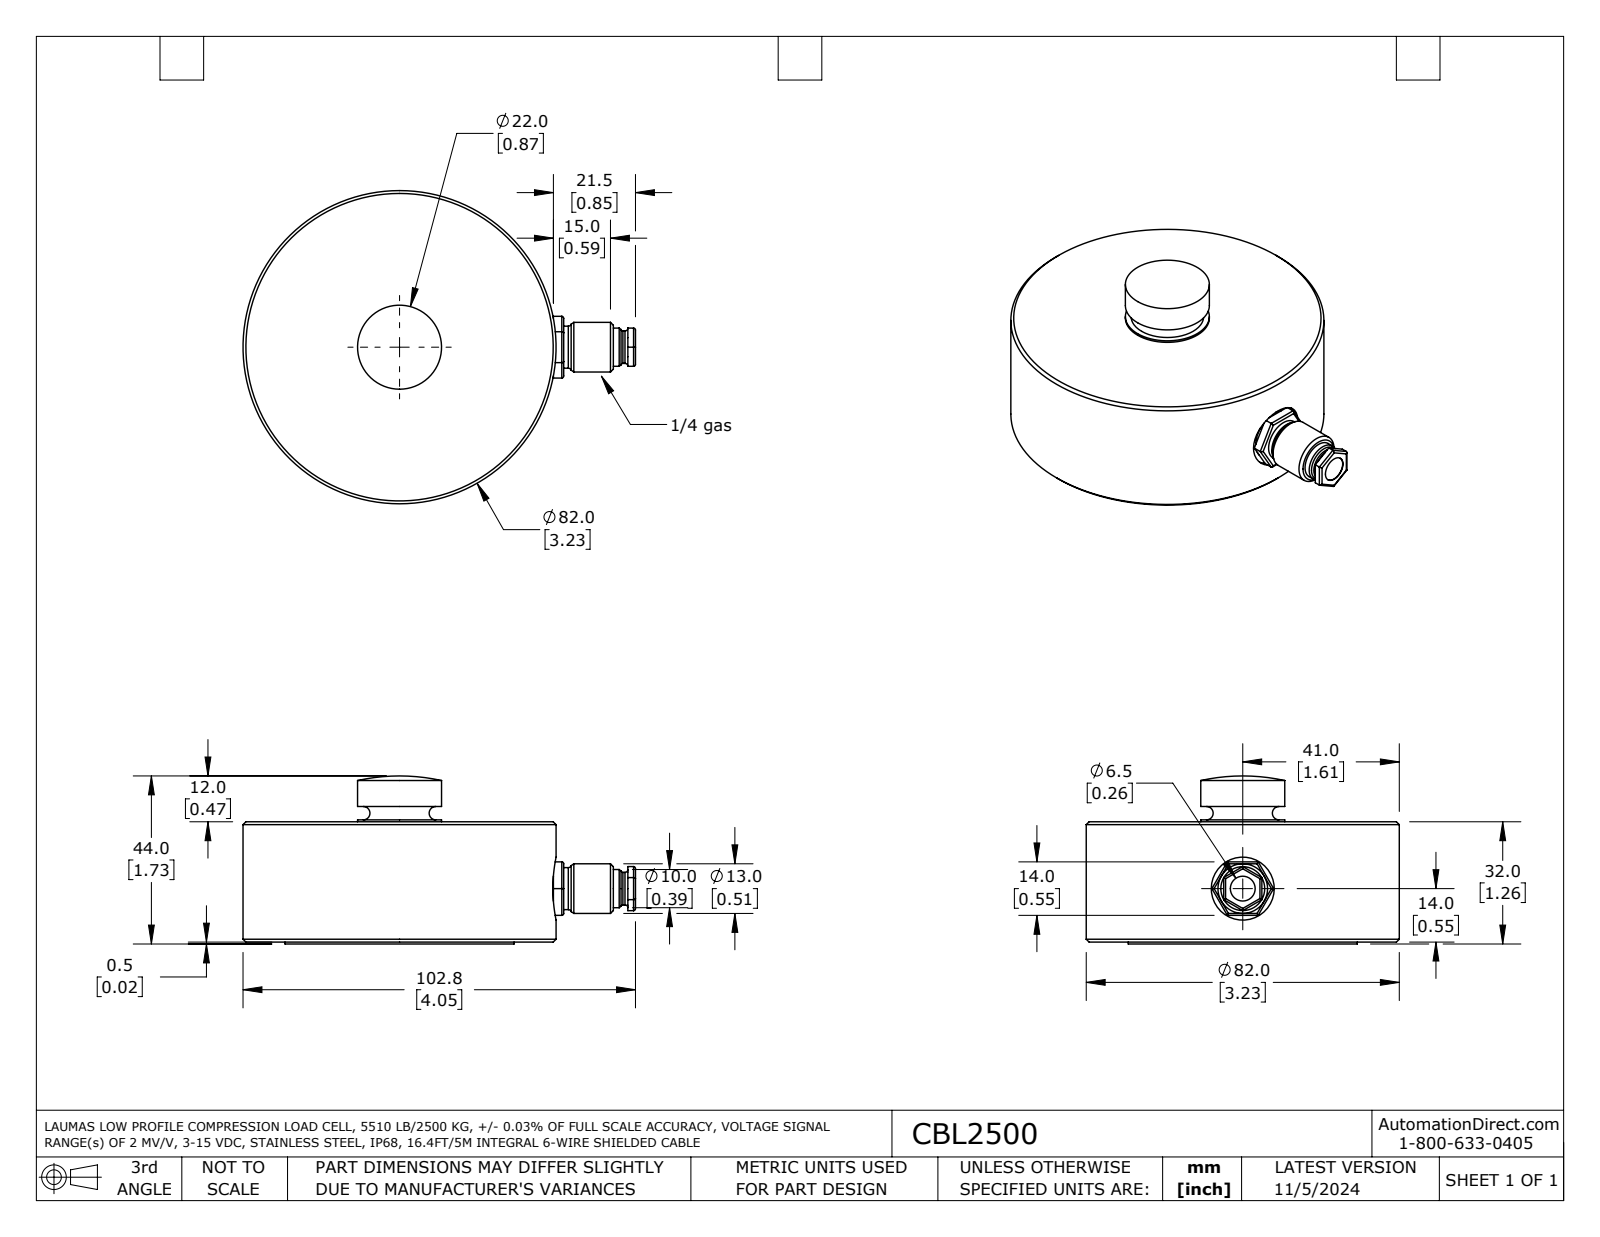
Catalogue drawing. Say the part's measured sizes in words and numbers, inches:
The part is named "CBL2500". Its 3-D file was written by "SolidWorks 2021 (AUTOMOTIVE_DESIGN)". It is 2 solids with 86 faces: 31 planar, 36 cylindrical and 19 other. Overall it measures 4.047 by 3.228 by 1.732 inches. Its volume is 10.42 cubic inches and its surface area 32.65 square inches. Round holes: 1 of diameter 0.256, 1 of diameter 0.65, 1 of diameter 2.15. Round bosses or shafts: 1 of diameter 3.228, 1 of diameter 2.362, 1 of diameter 0.866, 1 of diameter 0.531, 1 of diameter 0.512, 1 of diameter 0.433, 1 of diameter 0.394, 1 of diameter 0.335. Partial cylindrical surfaces (rounded edges, fillets, slot ends): 12 of radius 0.02. The main face-to-face distances are 1.211, 0.03, 1.24, 0.02, 1.26, 0.049, 0.138, 1.28, 1.23, 1.417.
